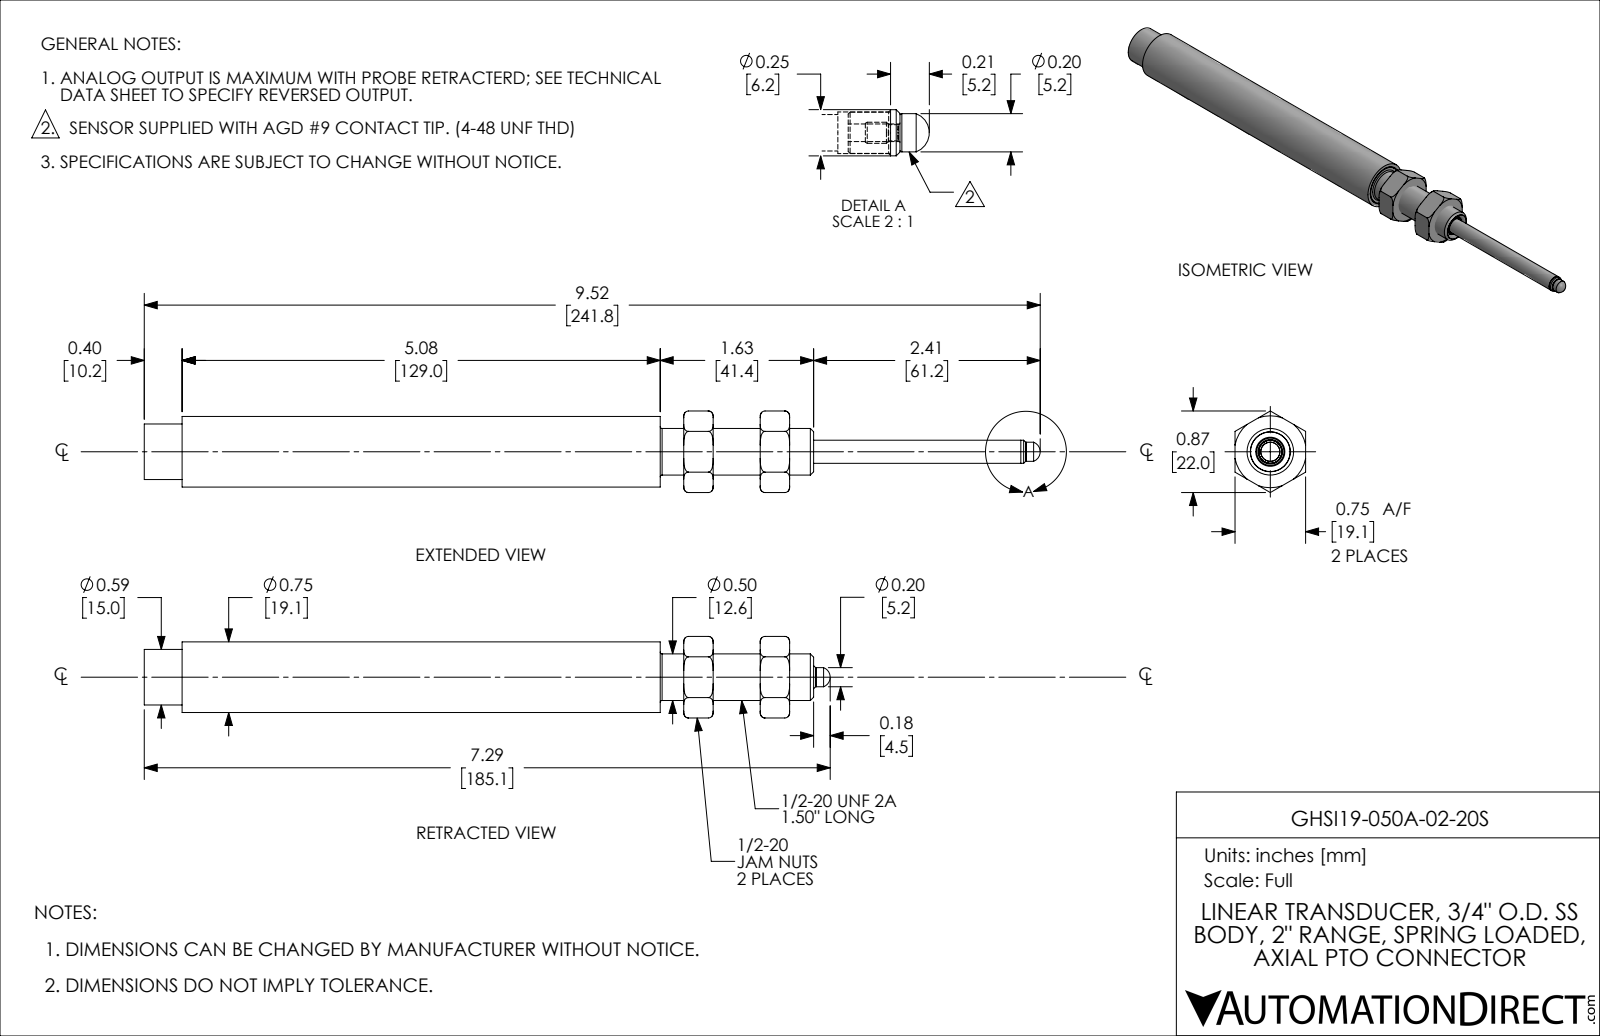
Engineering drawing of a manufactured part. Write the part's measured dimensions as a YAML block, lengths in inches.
part_name: "GHSI19-050A-02-20S"
step_written_by: "SolidWorks 2019 (AUTOMOTIVE_DESIGN)"
units: inches
bodies: {solids: 11, faces: 187, planar: 77, cylindrical: 65, other: 45}
overall_size: [7.288, 0.866, 0.75]
volume: 1.442
surface_area: 45.48
round_holes:
  - {diameter: 0.093, count: 1}
  - {diameter: 0.156, count: 1}
  - {diameter: 0.193, count: 1}
  - {diameter: 0.221, count: 1}
  - {diameter: 0.249, count: 1}
  - {diameter: 0.302, count: 1}
  - {diameter: 0.31, count: 1}
  - {diameter: 0.453, count: 1}
  - {diameter: 0.52, count: 1}
  - {diameter: 0.62, count: 1}
  - {diameter: 0.625, count: 1}
  - {diameter: 0.65, count: 1}
round_bosses_or_shafts:
  - {diameter: 0.03, count: 6}
  - {diameter: 0.75, count: 1}
  - {diameter: 0.725, count: 1}
  - {diameter: 0.672, count: 1}
  - {diameter: 0.624, count: 1}
  - {diameter: 0.59, count: 1}
  - {diameter: 0.495, count: 1}
  - {diameter: 0.375, count: 1}
partial_cylinders:
  - {radius: 0.011, count: 2}
  - {radius: 0.04, count: 2}
  - {radius: 0.133, count: 1}
  - {radius: 0.156, count: 1}
  - {radius: 0.275, count: 1}
face_to_face_distances: [0.813, 0.313, 0.75, 1.125, 0.5, 0.75, 5.352, 5.665, 6.165, 6.477]
